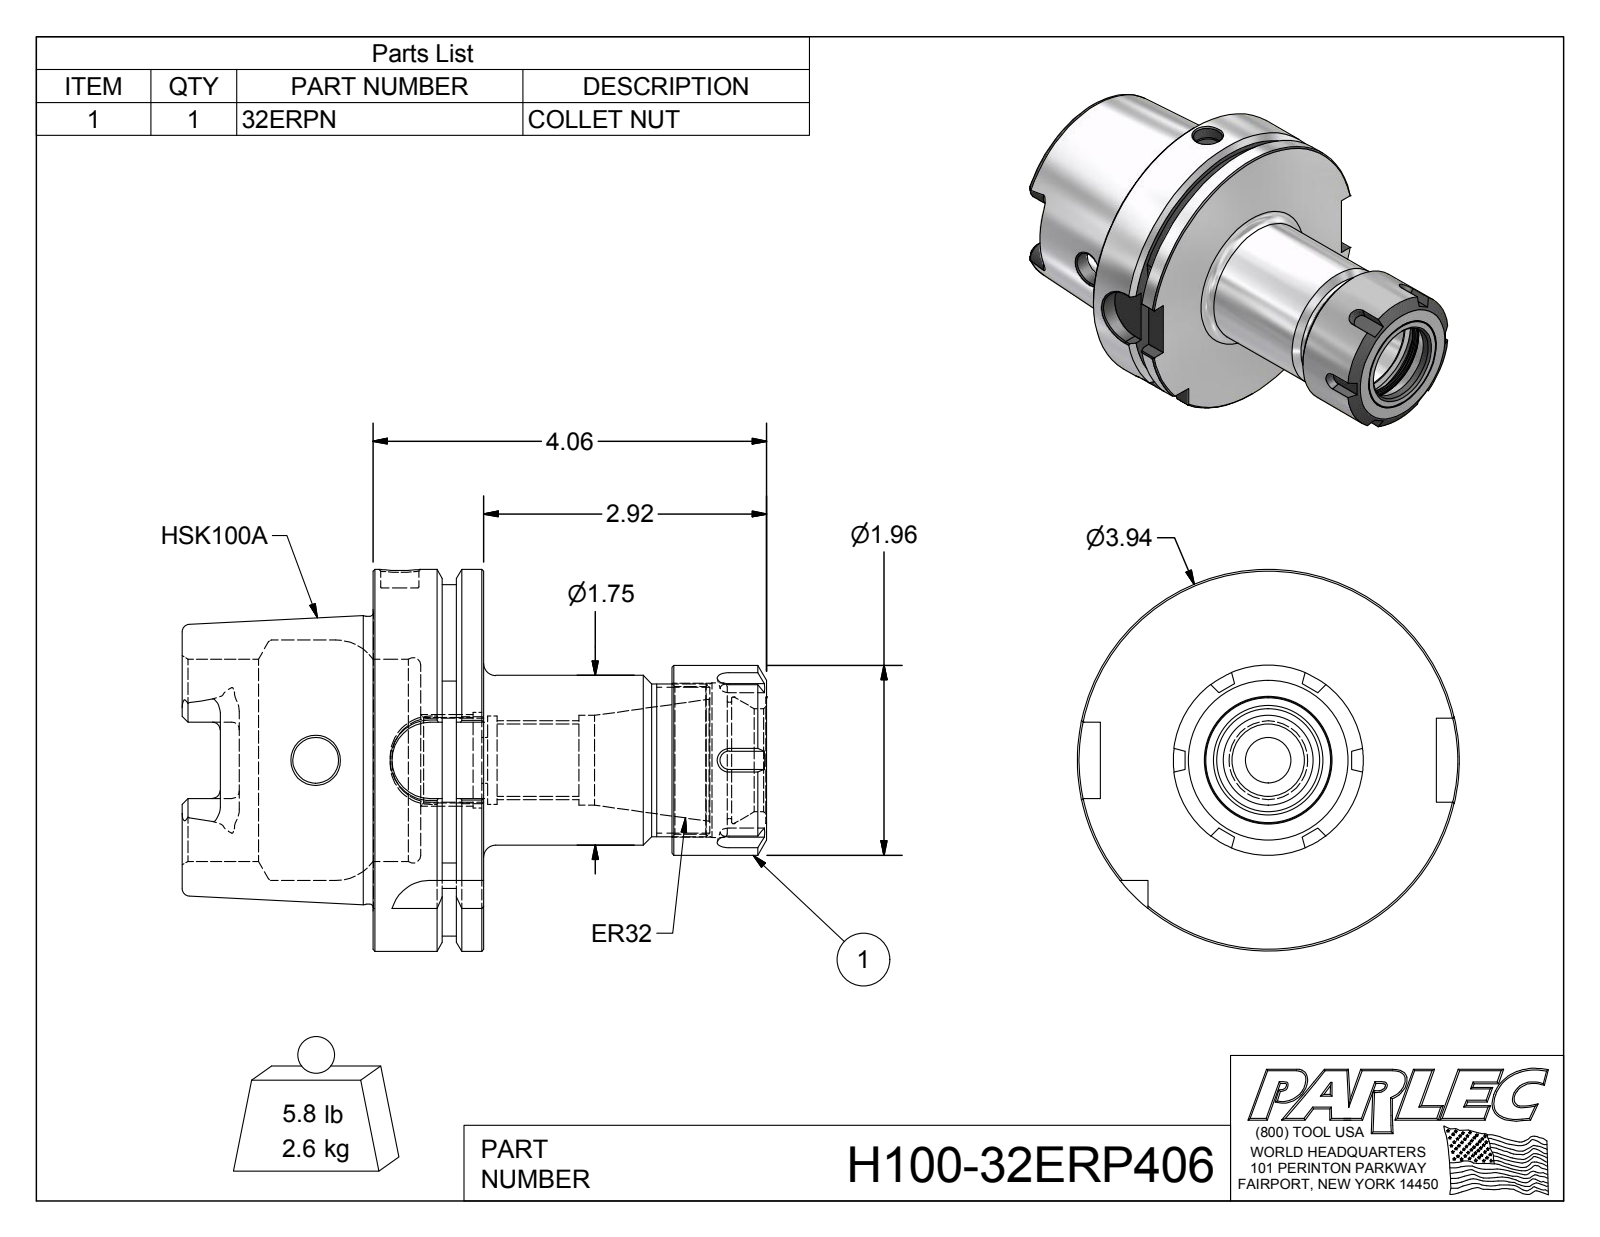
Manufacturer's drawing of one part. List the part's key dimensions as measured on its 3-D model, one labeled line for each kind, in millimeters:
Part name (STEP PRODUCT): H100-32ERP406; H100-32ER4-1; 32ERPN
STEP written by: Autodesk Inventor 2012 (AUTOMOTIVE_DESIGN)
Units: millimetres
Bodies: 2 solids, 178 faces (68 planar, 42 cylindrical, 68 other)
Overall size (bounding box): 153.1 × 100 × 100
Volume: 335 600 mm³ · Surface area: 71 230 mm²
Round holes (diameter × count): ⌀12 ×2, ⌀10 ×1, ⌀18.9 ×1, ⌀22.4 ×1, ⌀23.2 ×1, ⌀23.5 ×1, ⌀25 ×1, ⌀27 ×1, ⌀30.5 ×1, ⌀33.1 ×1, ⌀38.7 ×1, ⌀40.5 ×1
Round bosses / shafts (diameter × count): ⌀100 ×1, ⌀75.4 ×1, ⌀49.7 ×1, ⌀44.5 ×1, ⌀40 ×1
Partial cylindrical surfaces — rounded edges, fillets, slot ends (radius × count): R2 ×6, R4.9 ×4, R10 ×4, R46 ×1
Main face-to-face distances: 29, 12.5, 16.5, 50, 62.5, 79, 153.1, 103.1, 90.6, 74.1
